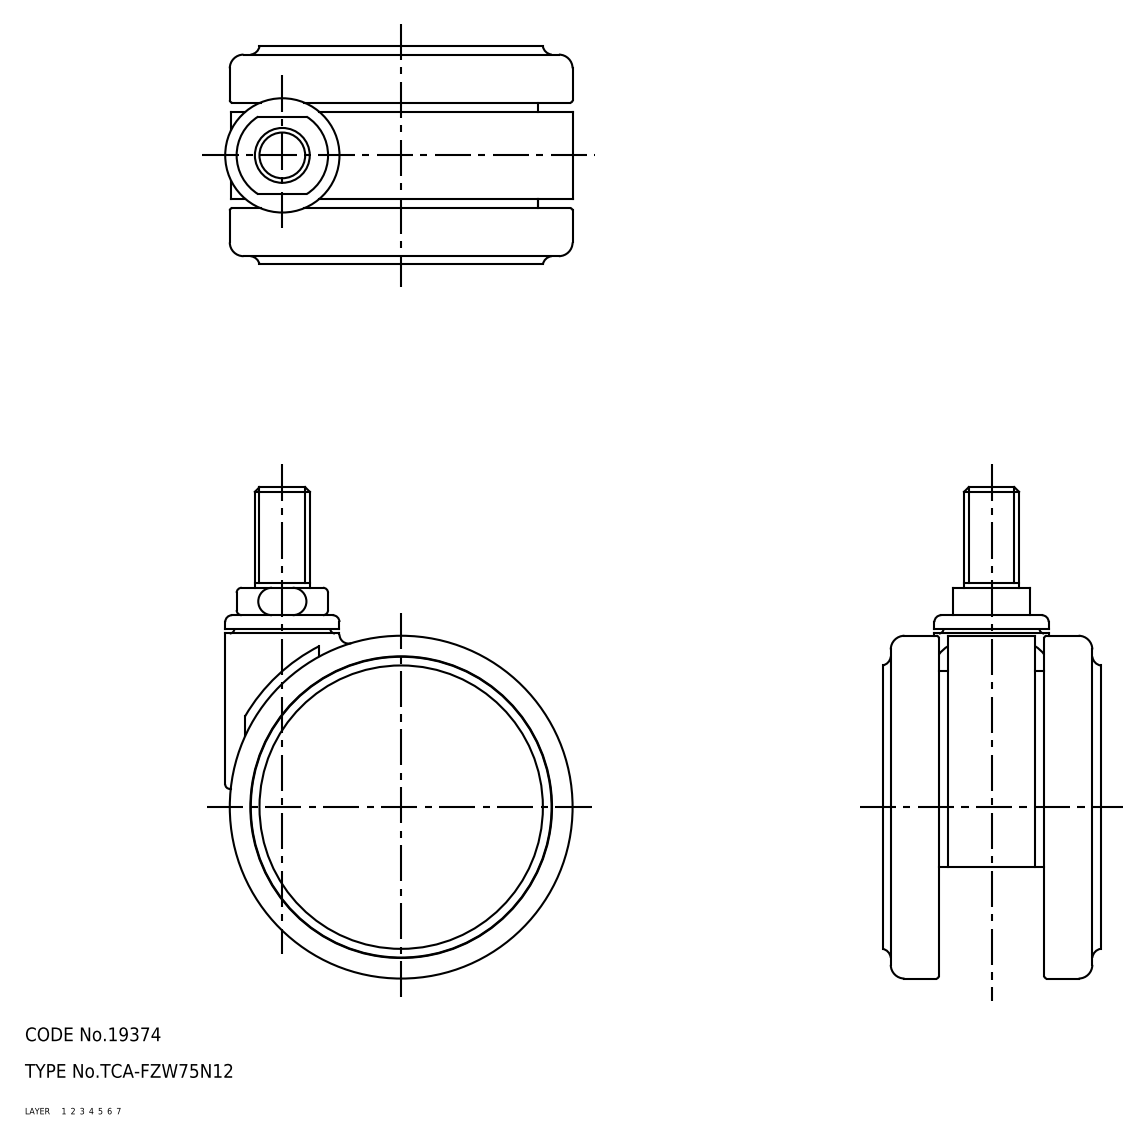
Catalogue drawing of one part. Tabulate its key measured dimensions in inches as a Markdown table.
| quantity | value |
| --- | --- |
| part name | TCA-FZW75N12; caster |
| STEP written by | SolidWorks 2015 (AUTOMOTIVE_DESIGN) |
| units | inches |
| bodies | 1 solid, 1801 faces (425 planar, 766 cylindrical, 610 other) |
| overall size | 4.232 × 2.992 × 1.878 |
| volume | 6.964 in³ |
| surface area | 107.1 in² |
| round holes (diameter × count) | 0.256 × 1, 0.315 × 1, 0.319 × 1, 0.335 × 1, 0.402 × 1, 0.433 × 1, 0.669 × 1, 0.713 × 1, 0.748 × 1, 0.89 × 1, 2.323 × 1, 2.48 × 1 |
| round bosses / shafts (diameter × count) | 0.63 × 2, 2.591 × 1, 2.126 × 1, 1.024 × 1, 0.984 × 1, 0.551 × 1, 0.472 × 1, 0.394 × 1 |
| partial cylindrical surfaces (radius × count) | 0.02 × 119, 0.039 × 79, 0.012 × 60, 0.008 × 16, 0.079 × 12, 0.118 × 1, 0.157 × 1, 0.236 × 1 |
| main face-to-face distances | 0.059, 1.819, 0.071, 0.13, 1.748, 1.689, 1.264, 0.354, 1.394, 0.484 |
